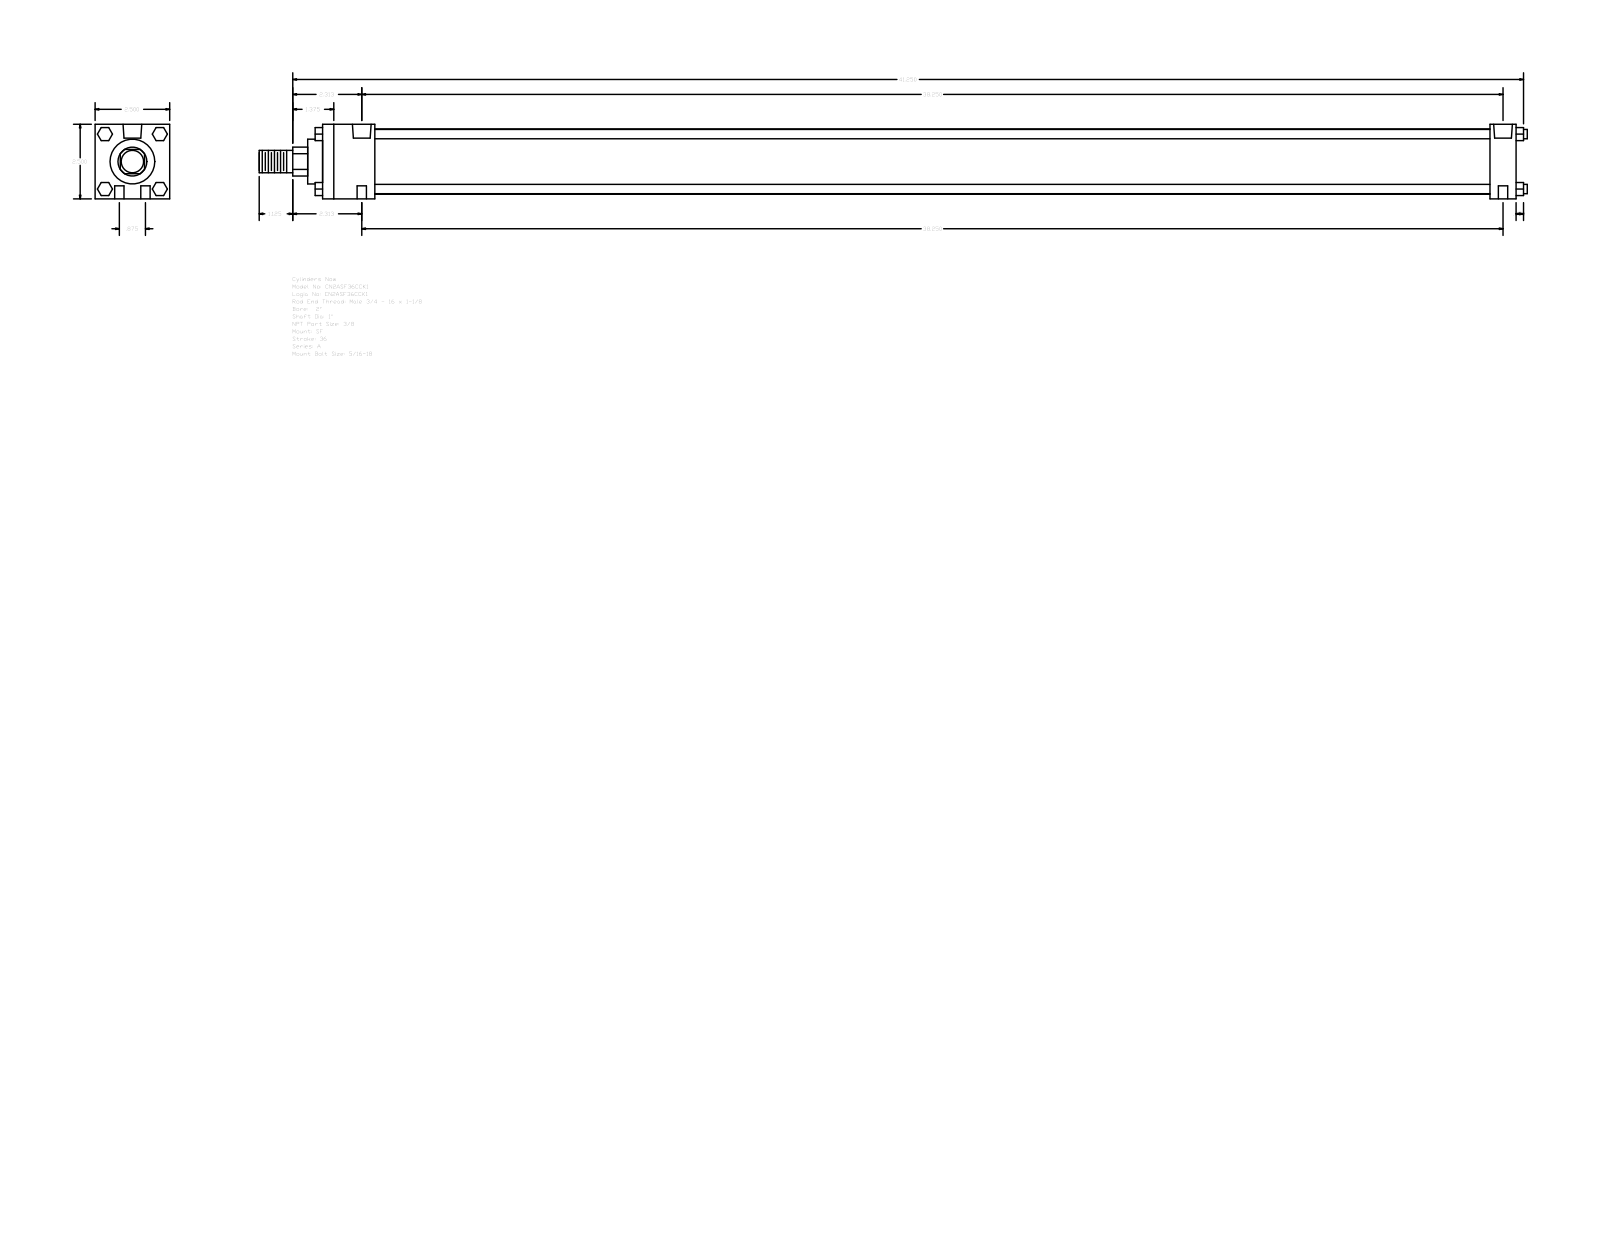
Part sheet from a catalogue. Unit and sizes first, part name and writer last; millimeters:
Units: millimetres
Overall size (bounding box): 1079.5 × 63.5 × 63.5
Round holes (diameter × count): ⌀7.94 ×4, ⌀5.56 ×2, ⌀15.93 ×2
Round bosses / shafts (diameter × count): ⌀7.94 ×4, ⌀55.63 ×1, ⌀38.1 ×1, ⌀25.4 ×1, ⌀19.05 ×1
Partial cylindrical surfaces — rounded edges, fillets, slot ends (radius × count): R12.29 ×1
Main face-to-face distances: 63.5, 1016, 993.77, 22.23, 44.45, 949.32, 971.55, 12.7, 1028.7, 6.35
Hole centre spacings: 11.11, 971.61, 971.55, 22.22, 971.8, 965.98
Bodies: 0 solids, 124 faces (94 planar, 30 cylindrical, 0 other)
Part name (STEP PRODUCT): A_SF__0200_1
STEP written by: GSSL Pune (CONFIG_CONTROL_DESIGN)
